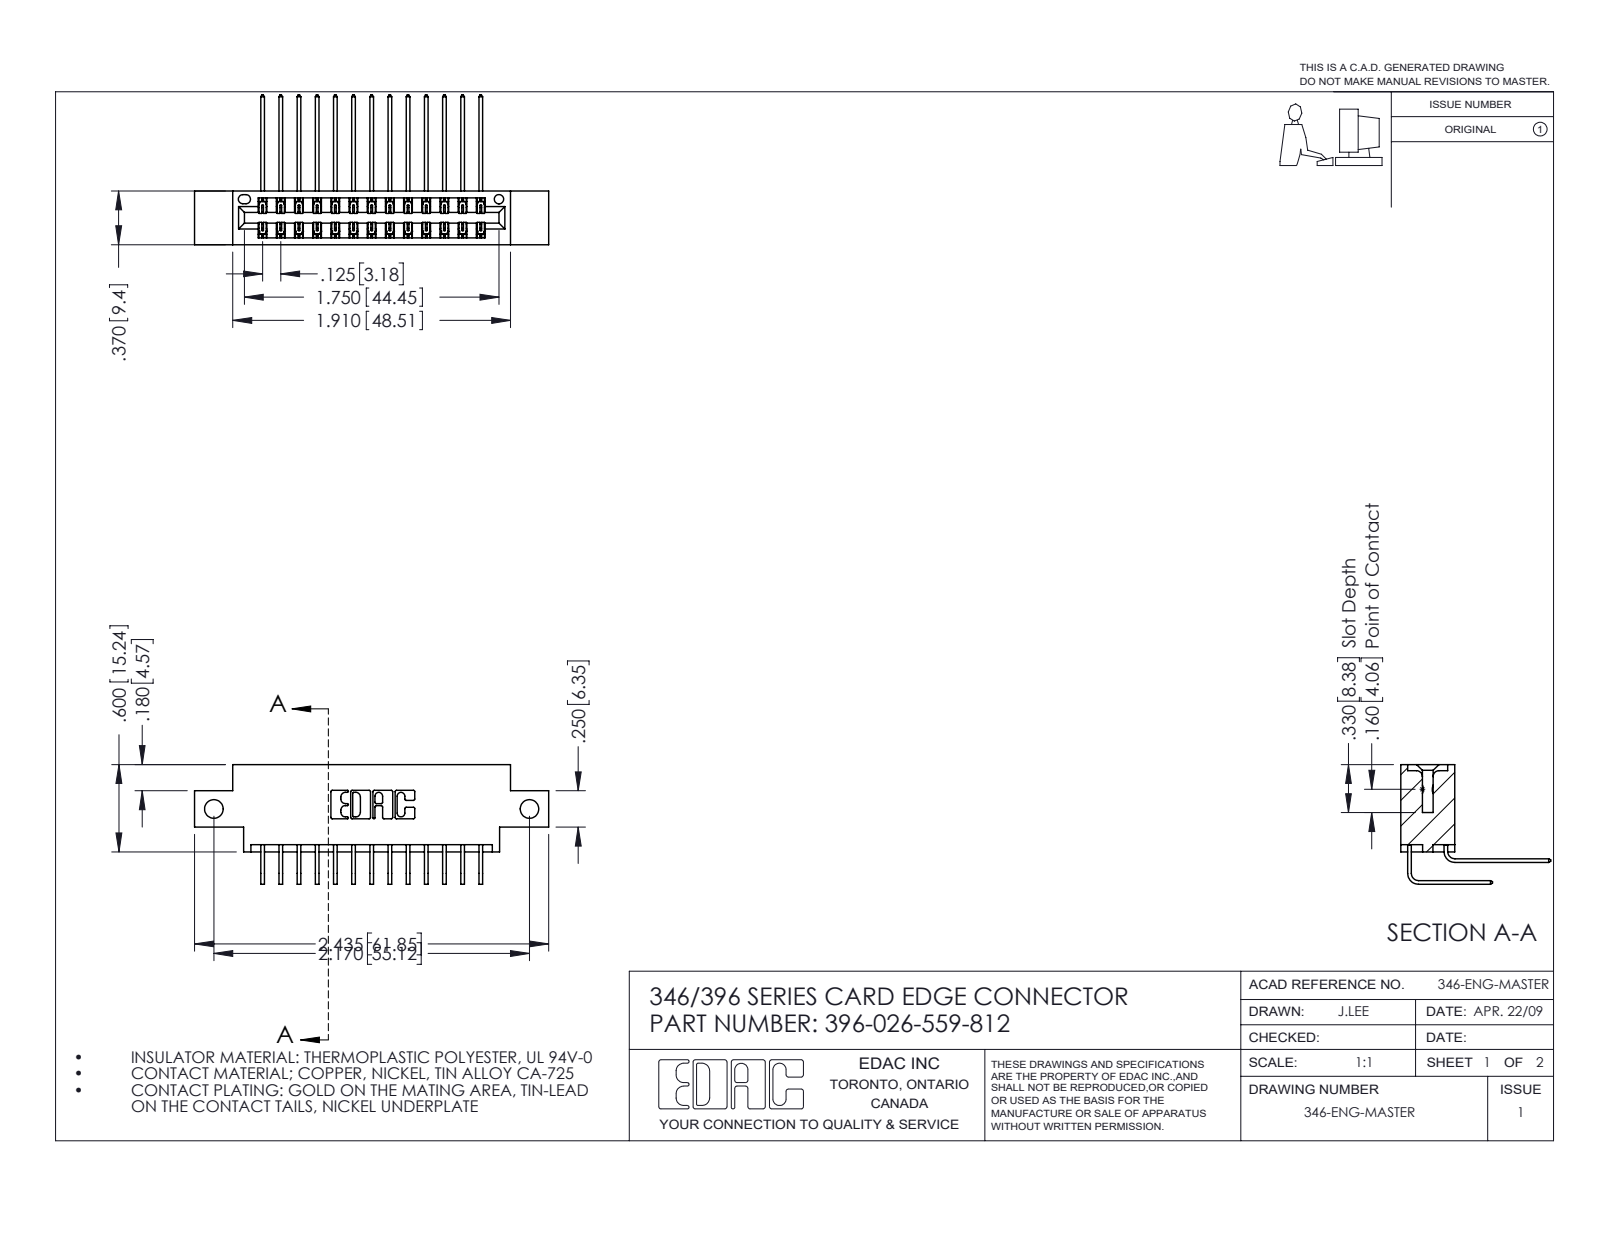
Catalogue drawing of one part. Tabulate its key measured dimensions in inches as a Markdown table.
| quantity | value |
| --- | --- |
| part name | 346 Part_0.170 Offset - Side Mount; 396-026-559-812; 345-292-001_558 559 Tail - 1; 345-292-001_559 Tail - 2 |
| STEP written by | SolidWorks 2016 (CONFIG_CONTROL_DESIGN) |
| units | inches |
| bodies | 27 solids, 1530 faces (1042 planar, 488 cylindrical, 0 other) |
| overall size | 2.435 × 1.03 × 0.823 |
| volume | 0.349 in³ |
| surface area | 12.65 in² |
| round holes (diameter × count) | 0.128 × 2, 0.064 × 1 |
| partial cylindrical surfaces (radius × count) | 0.006 × 39, 0.01 × 22, 0.007 × 6, 0.031 × 6, 0.026 × 3, 0.014 × 2, 0.022 × 2, 0.024 × 2 |
| main face-to-face distances | 0.048, 0.25, 0.322, 0.37, 0.025, 0.072, 0.298, 0.275, 0.15, 0.148 |
| hole center spacings | 2.17 |
